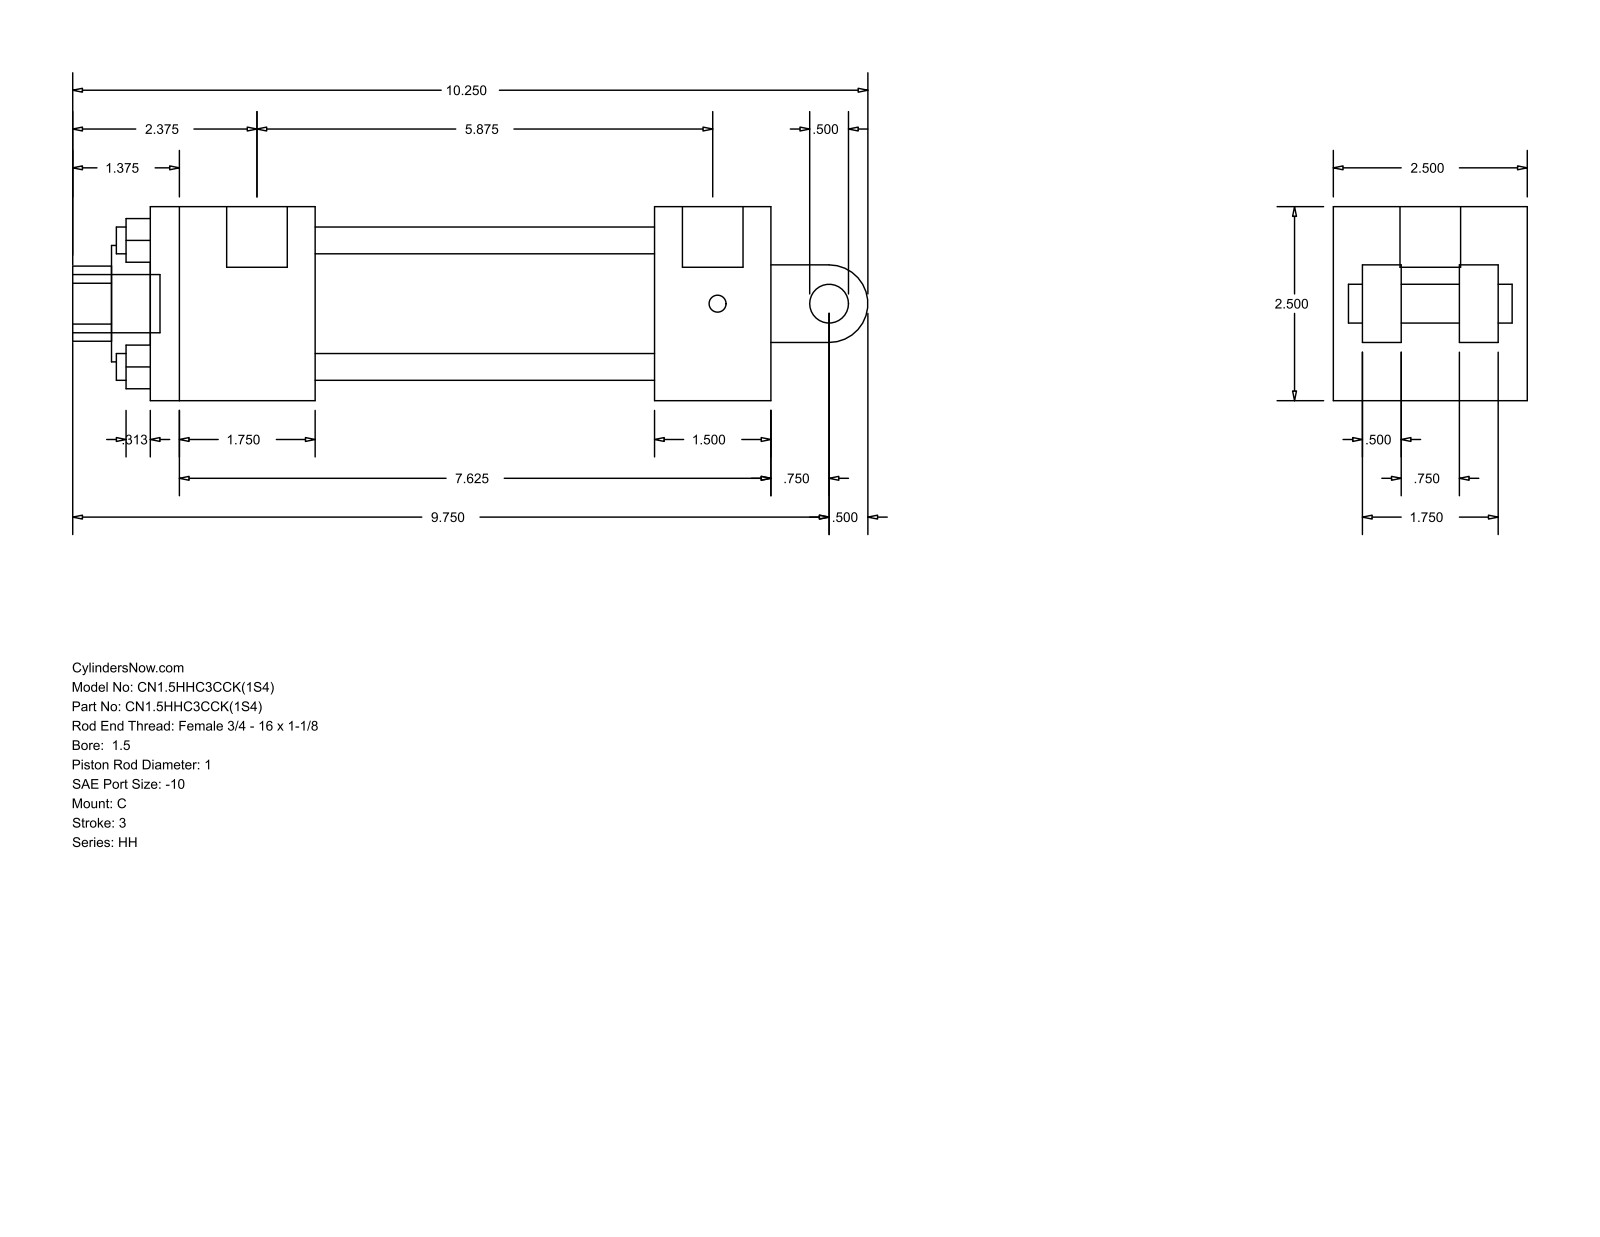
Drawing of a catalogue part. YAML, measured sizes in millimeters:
part_name: "HH_C__0150_1"
step_written_by: "GSSL Pune (CONFIG_CONTROL_DESIGN)"
units: millimeters
bodies: {solids: 0, faces: 99, planar: 70, cylindrical: 29, other: 0}
overall_size: [260.35, 63.5, 63.5]
round_holes:
  - {diameter: 8.76, count: 4}
  - {diameter: 5.56, count: 2}
  - {diameter: 19.84, count: 1}
  - {diameter: 25.4, count: 1}
  - {diameter: 38.1, count: 1}
  - {diameter: 44.45, count: 1}
round_bosses_or_shafts:
  - {diameter: 5.56, count: 2}
  - {diameter: 19.84, count: 1}
  - {diameter: 19.05, count: 1}
  - {diameter: 12.7, count: 1}
partial_cylinders:
  - {radius: 12.29, count: 1}
  - {radius: 12.7, count: 1}
face_to_face_distances: [63.5, 53.98, 111.12, 149.22, 38.1, 165.1, 203.2, 12.7, 22.22, 41.28]
hole_center_spacings: [29.27, 41.4, 58.55, 1.59]
